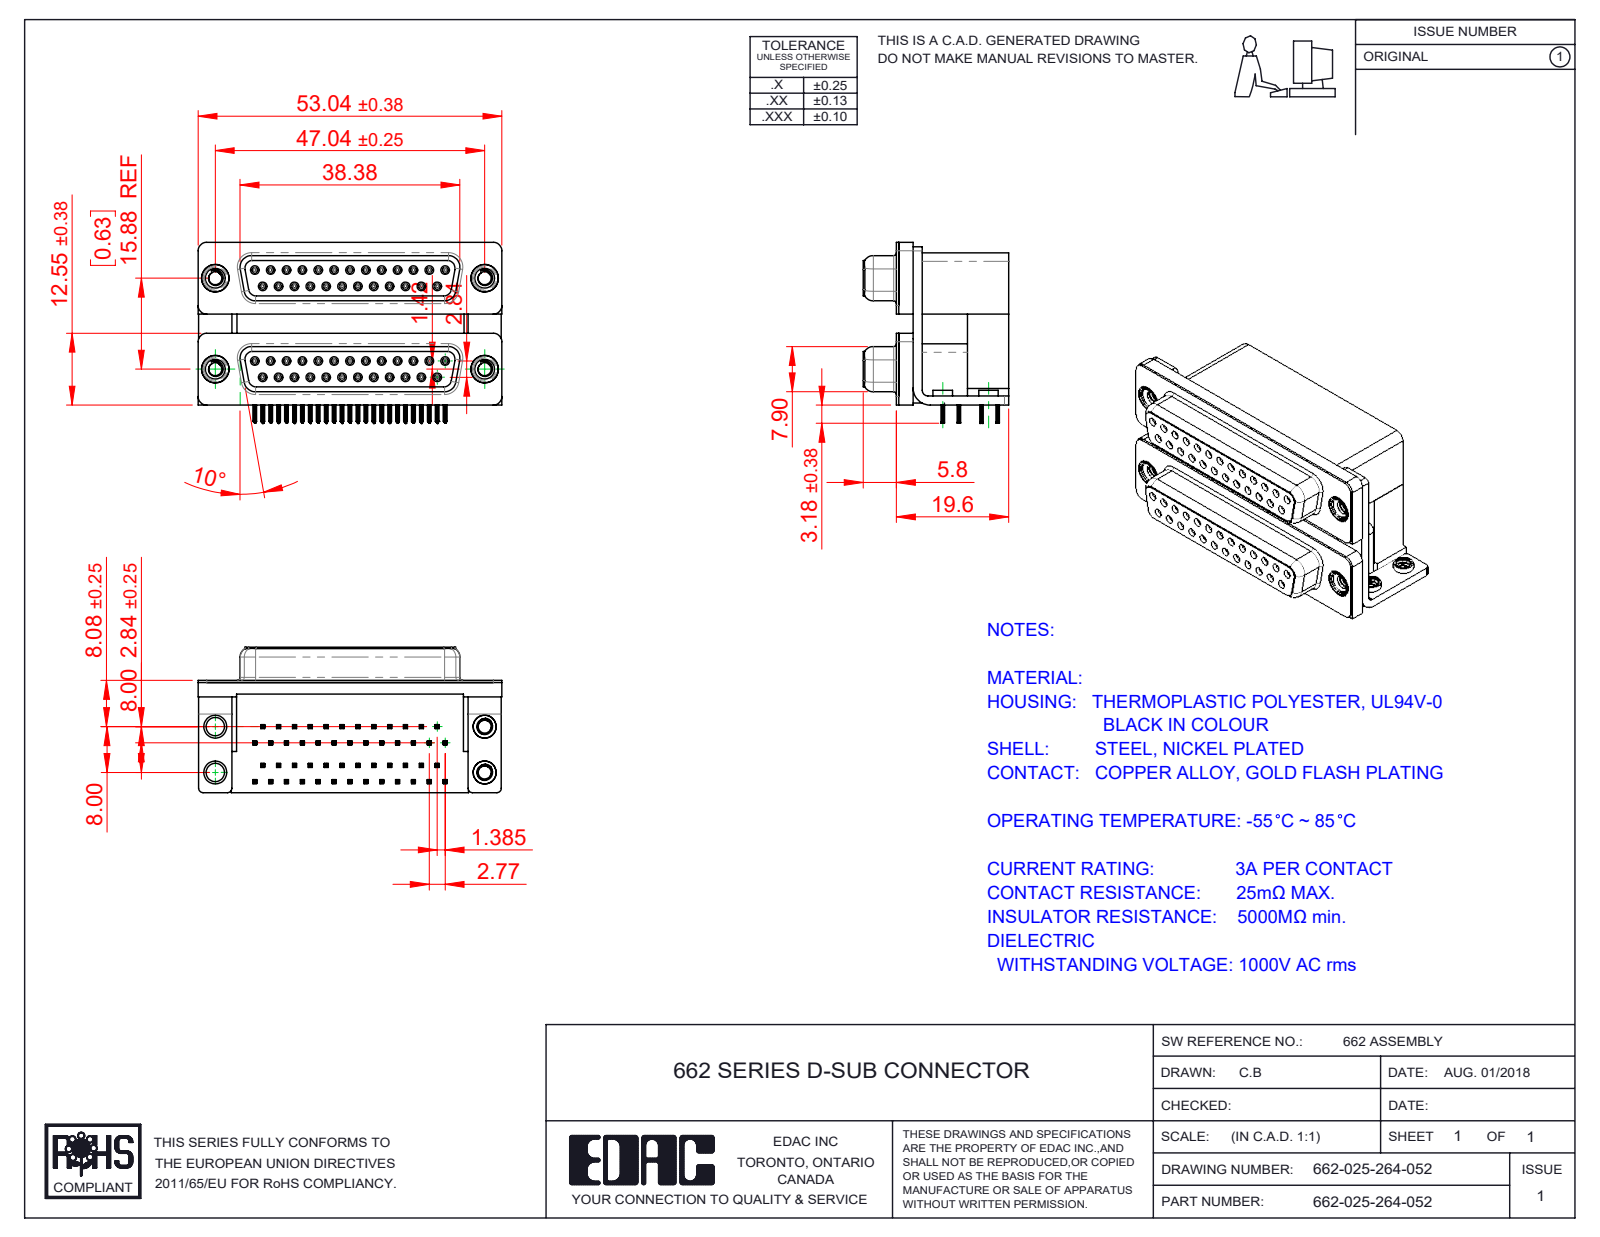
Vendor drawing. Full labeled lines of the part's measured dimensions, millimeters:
Part name (STEP PRODUCT): 662 Contact Bottom Lower; 662 Contact Top Upper_L; 662 4-40 Threaded Board Mount; 662 Shell_25 Contacts (+8 more)
STEP written by: SolidWorks 2020 (CONFIG_CONTROL_DESIGN)
Units: millimetres
Bodies: 65 solids, 7932 faces (3588 planar, 1880 cylindrical, 2464 other)
Overall size (bounding box): 53.04 × 31.61 × 25.4
Volume: 22 934 mm³ · Surface area: 25 240 mm²
Round holes (diameter × count): ⌀0.8 ×50, ⌀0.9 ×50, ⌀2.26 ×8, ⌀2.75 ×4, ⌀3.2 ×4, ⌀3.5 ×4, ⌀4 ×4, ⌀4.8 ×4, ⌀5 ×4
Round bosses / shafts (diameter × count): ⌀1.2 ×50, ⌀4.9 ×4, ⌀4.75 ×4, ⌀4 ×4, ⌀3.9 ×4, ⌀3.4 ×4
Partial cylindrical surfaces — rounded edges, fillets, slot ends (radius × count): R0.1 ×400, R0.15 ×200, R0.35 ×100, R0.34 ×50, R0.28 ×24, R1.35 ×18, R1.5 ×13, R0.5 ×8
Main face-to-face distances: 15.88, 19.2, 0.4, 7.2, 12, 10.7, 6.2, 16.7, 9.5, 2.5
Hole centre spacings: 3.16, 2.77, 5.54, 11.08, 8.31, 5.03, 13.85, 7.48
